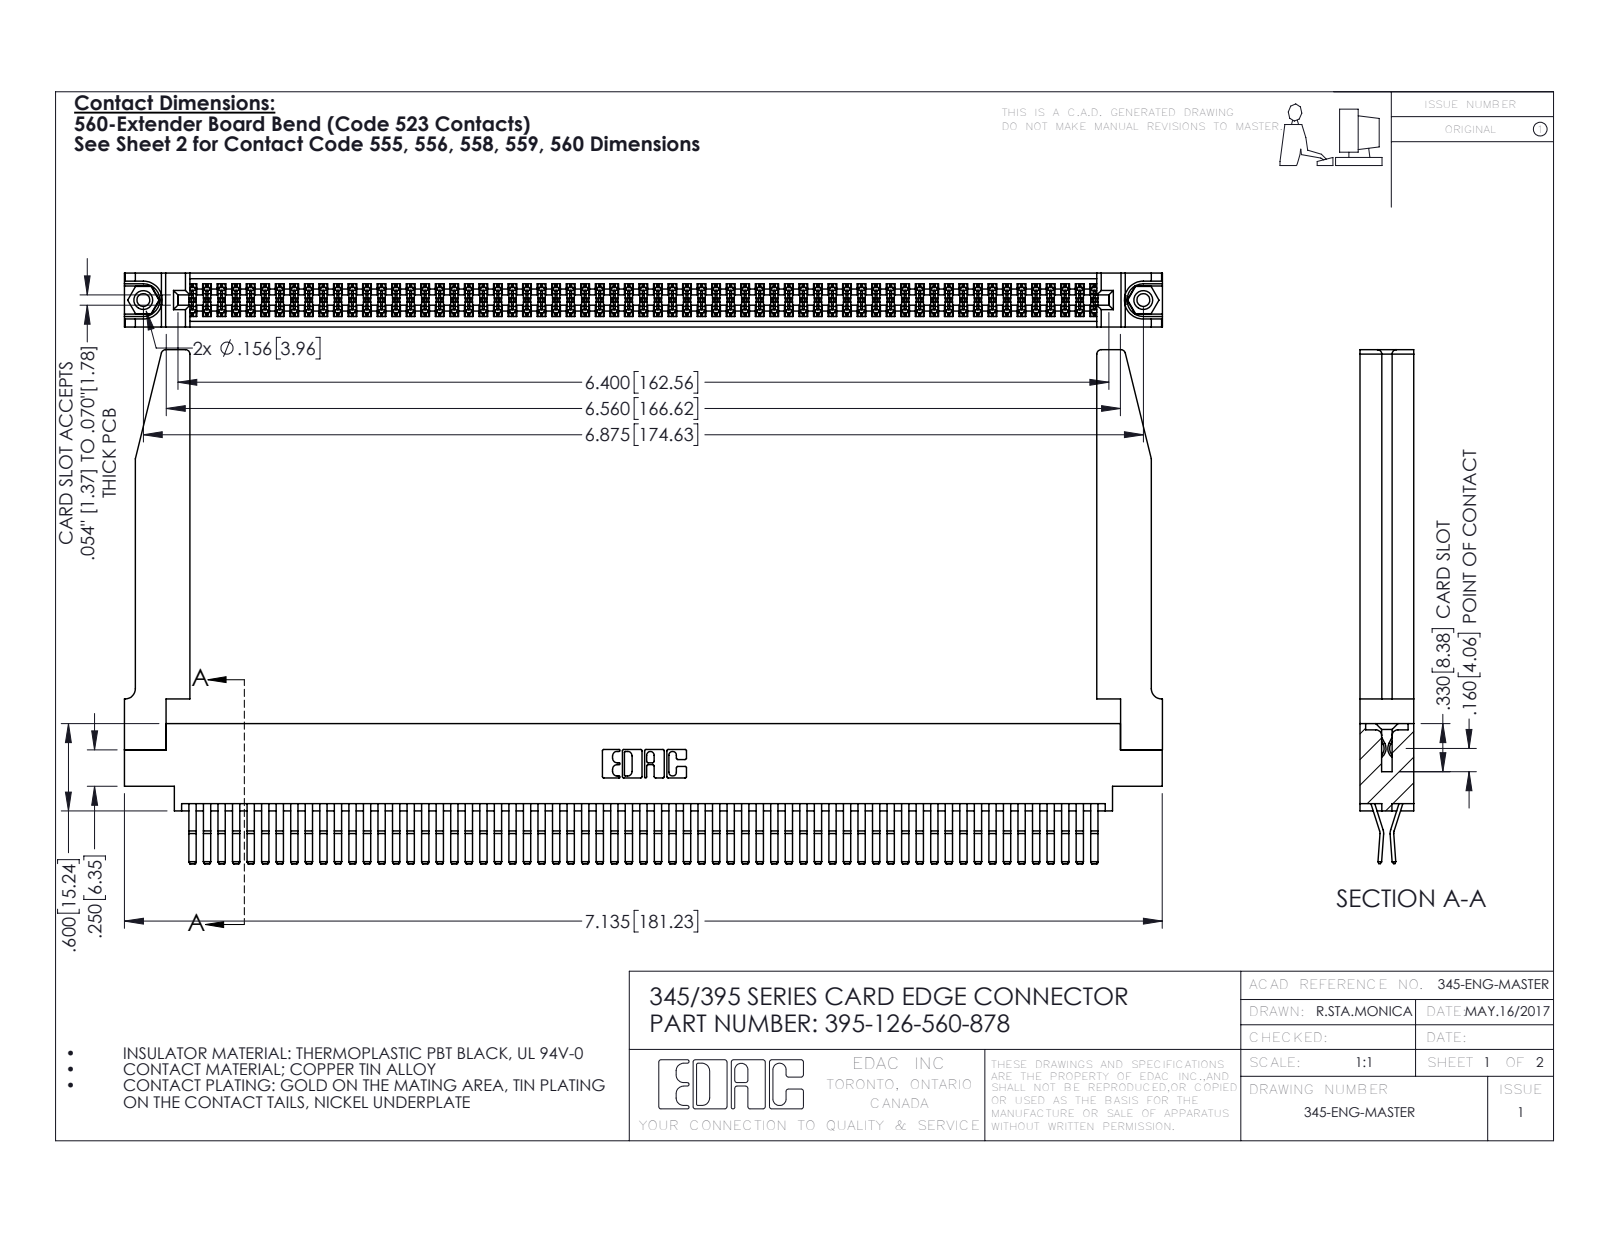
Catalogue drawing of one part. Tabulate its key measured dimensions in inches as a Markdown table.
| quantity | value |
| --- | --- |
| part name | 345 Part_0.170 Offset - 0.156 Dia-TH; 345-292-001_560 Tail; 395-126-560-878; 345-220-078_345-220-078 (+1 more) |
| STEP written by | SolidWorks 2016 (CONFIG_CONTROL_DESIGN) |
| units | inches |
| bodies | 131 solids, 6916 faces (4384 planar, 2480 cylindrical, 52 other) |
| overall size | 7.136 × 3.532 × 0.37 |
| volume | 1.604 in³ |
| surface area | 57.16 in² |
| round holes (diameter × count) | 0.089 × 2, 0.125 × 2, 0.156 × 2, 0.064 × 1 |
| round bosses / shafts (diameter × count) | 0.155 × 2 |
| partial cylindrical surfaces (radius × count) | 0.006 × 190, 0.01 × 22, 0.03 × 8, 0.007 × 6, 0.031 × 6, 0.026 × 3, 0.01 × 2, 0.014 × 2 |
| main face-to-face distances | 0.072, 0.37, 0.298, 0.025, 0.098, 0.272, 0.2, 0.225, 0.175, 0.148 |
| hole center spacings | 0.27, 6.639, 6.875 |
